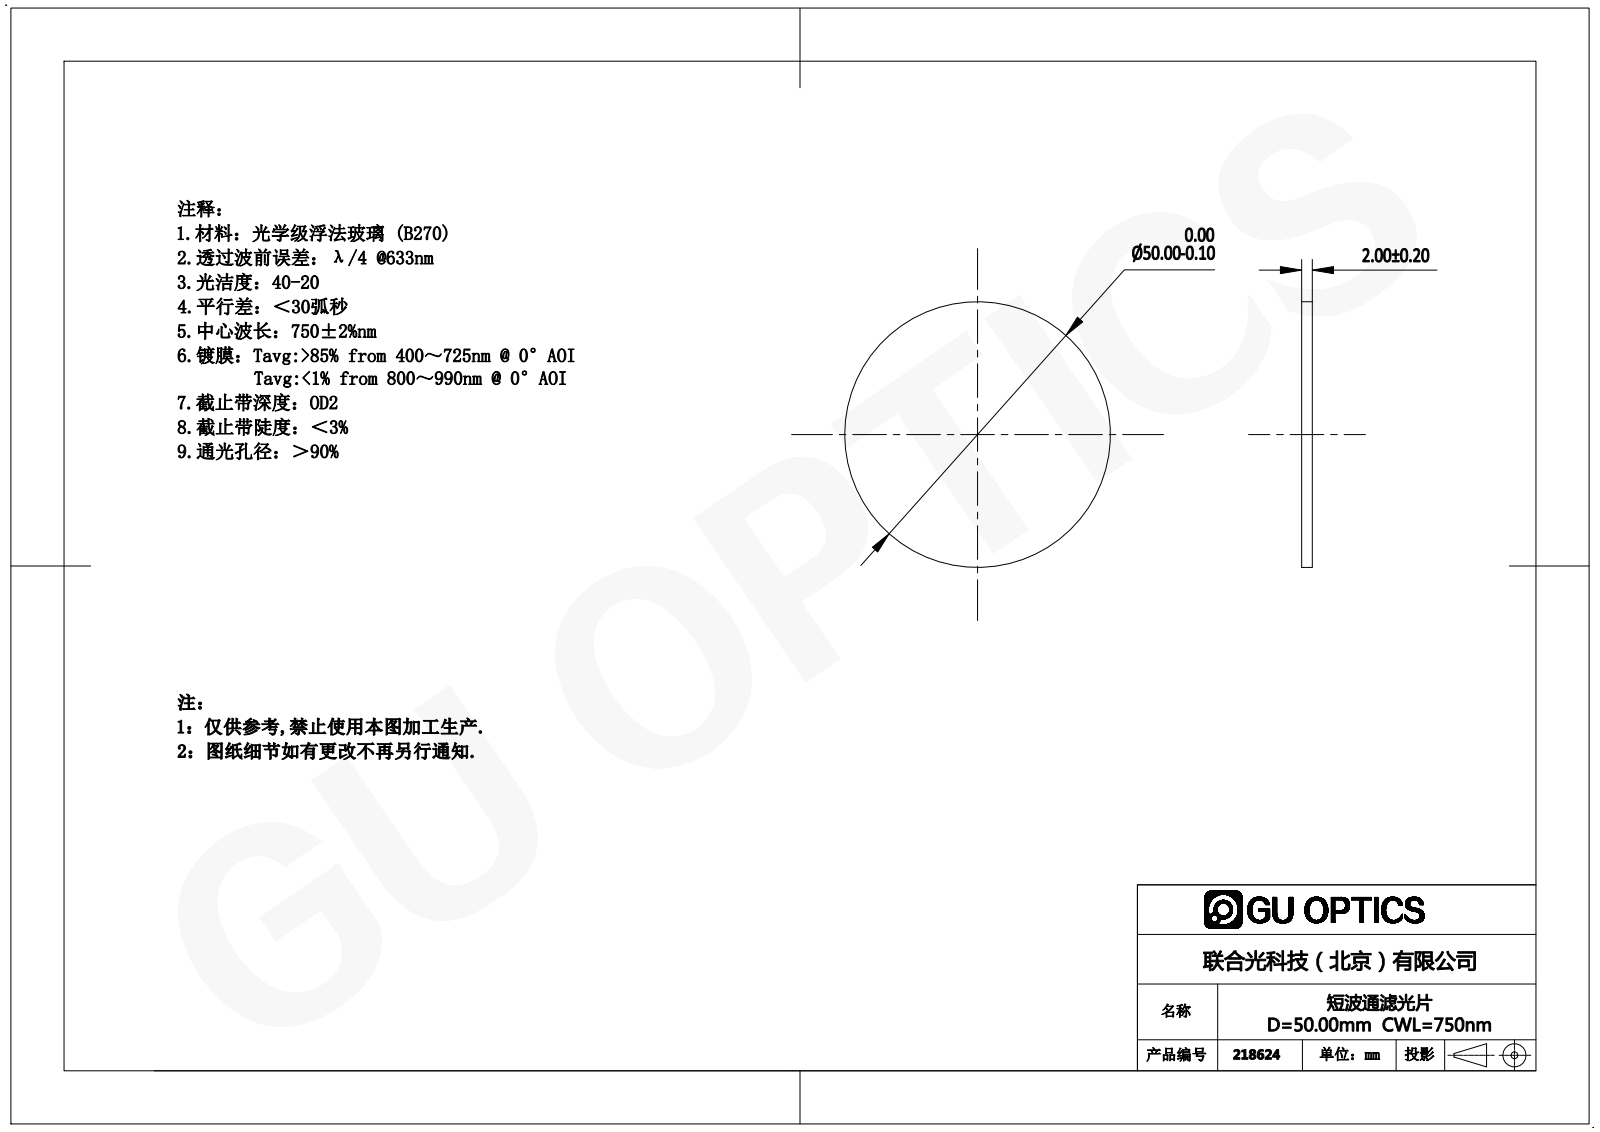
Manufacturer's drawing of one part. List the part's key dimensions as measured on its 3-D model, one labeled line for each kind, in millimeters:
Part name (STEP PRODUCT): 218617
STEP written by: SolidWorks 2016 (AUTOMOTIVE_DESIGN)
Units: millimetres
Bodies: 1 solid, 4 faces (2 planar, 2 cylindrical, 0 other)
Overall size (bounding box): 50 × 50 × 2
Volume: 3 927 mm³ · Surface area: 4 241 mm²
Round bosses / shafts (diameter × count): ⌀50 ×1
Main face-to-face distances: 2
